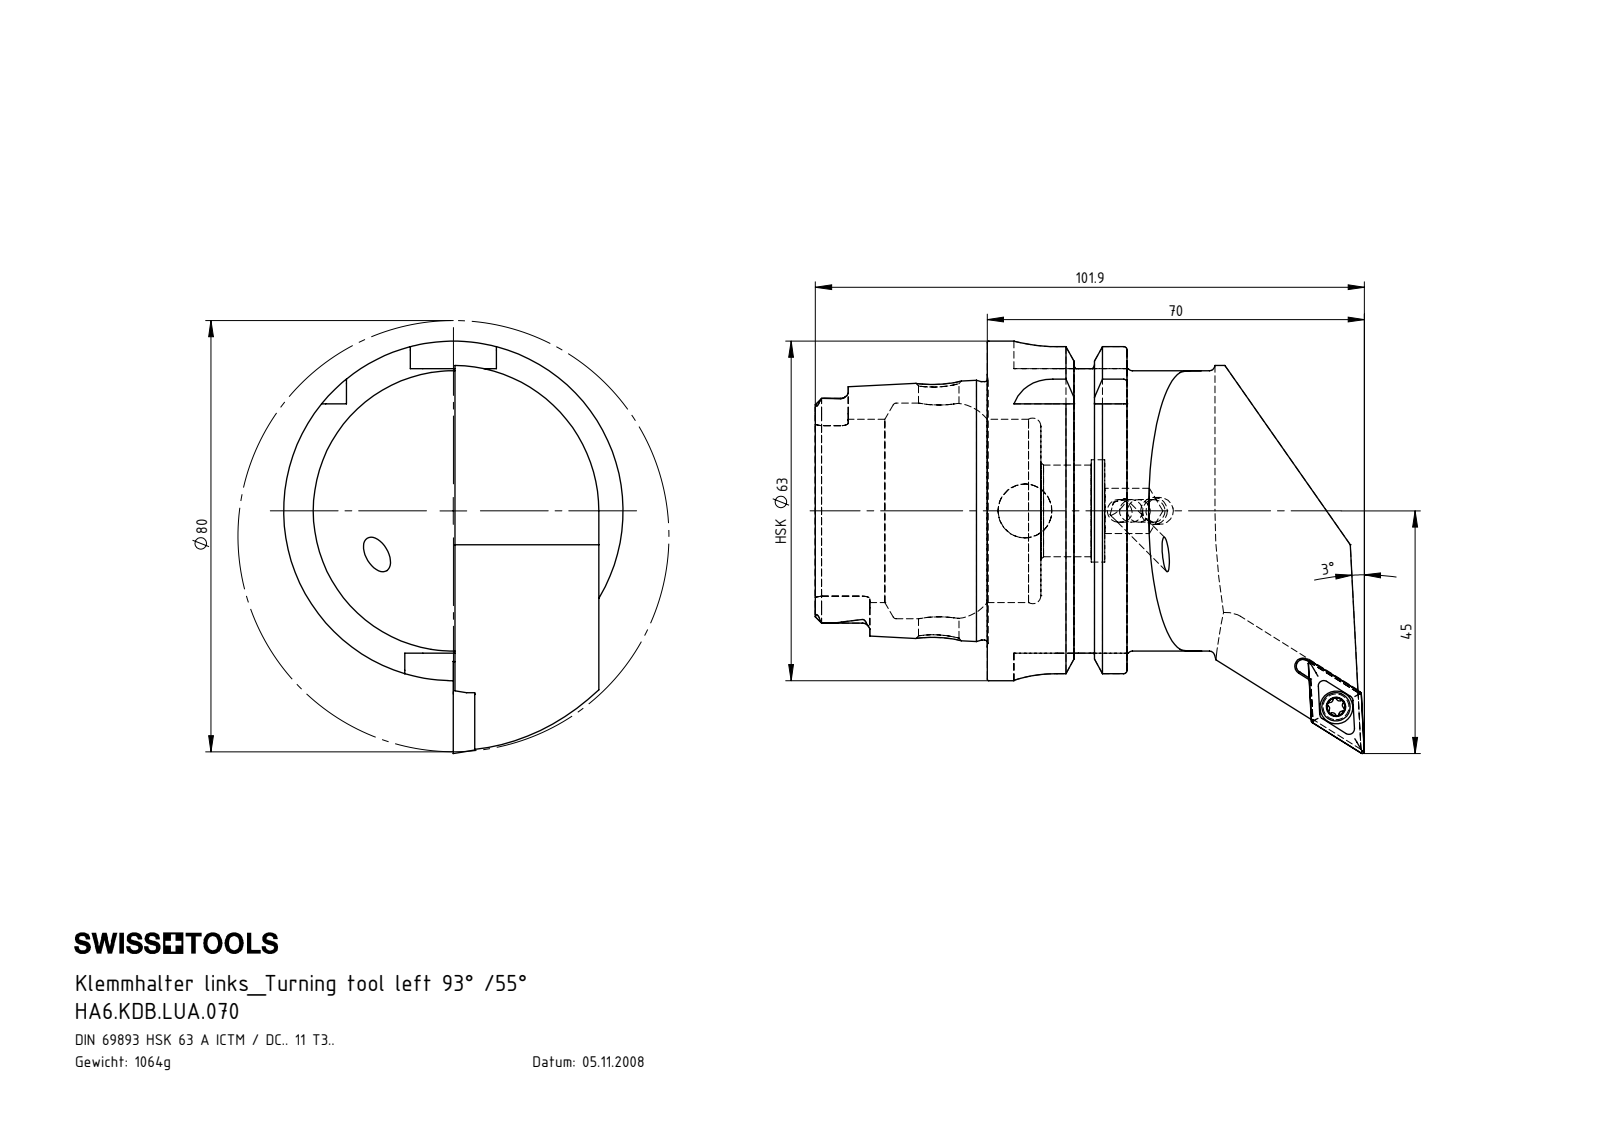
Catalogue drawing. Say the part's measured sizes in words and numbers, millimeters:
The part is named "HA6-KDB.LUA.070; KVT_MB_600_050; WCB-ER2.001.009_A; DCMT11T304 (+1 more)". Its 3-D file was written by "SolidWorks 2012 (CONFIG_CONTROL_DESIGN)". It is 5 solids with 309 faces: 78 planar, 90 cylindrical and 141 other. Overall it measures 101.9 by 76.51 by 63 millimeters. Its volume is 135 327 cubic millimeters and its surface area 29 966 square millimeters. Round holes: 2 of diameter 4.2, 1 of diameter 3.3, 1 of diameter 4, 1 of diameter 4.4, 1 of diameter 5, 1 of diameter 6.1, 1 of diameter 7.5, 1 of diameter 8.4, 1 of diameter 10, 1 of diameter 17, 1 of diameter 19, 1 of diameter 34. Round bosses or shafts: 1 of diameter 63, 1 of diameter 54.95, 1 of diameter 52, 1 of diameter 47.94, 1 of diameter 5.25, 1 of diameter 5, 1 of diameter 4. Partial cylindrical surfaces (rounded edges, fillets, slot ends): 6 of radius 0.34, 6 of radius 0.59, 6 of radius 1.4, 4 of radius 8, 2 of radius 2.82, 2 of radius 2.88, 1 of radius 1.25, 1 of radius 6. The main face-to-face distances are 26.7, 25.95, 16, 9.95, 31.9, 41.85, 57.85, 52.8, 21.8, 11.85. The hole center spacings are 68.23, 68.34.
